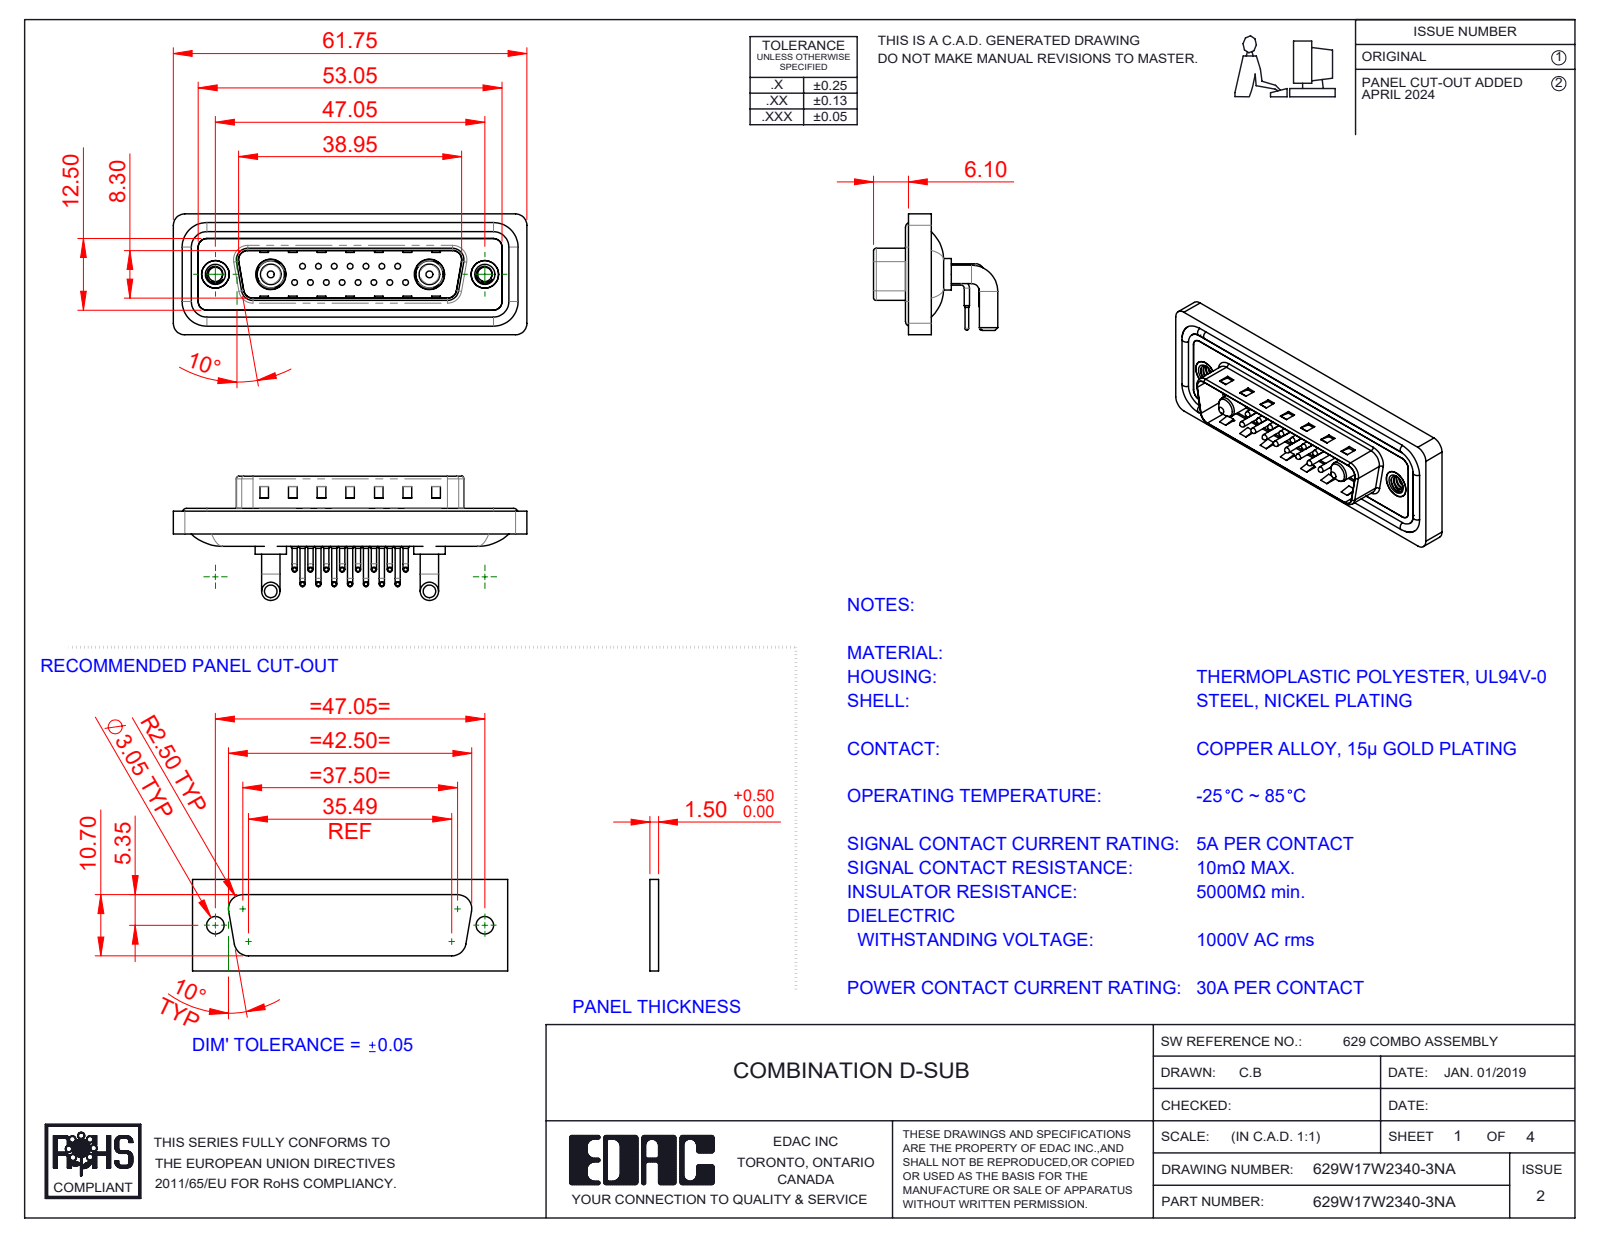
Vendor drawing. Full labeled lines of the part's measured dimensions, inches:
Part name (STEP PRODUCT): 629Combo Contact Row 2; 629Combo Contact Row 1; Power Pin_30A RA; 629Combo Shell Rear_25 Contacts (+5 more)
STEP written by: SolidWorks 2023 (CONFIG_CONTROL_DESIGN)
Units: inches
Bodies: 26 solids, 2213 faces (1189 planar, 768 cylindrical, 256 other)
Overall size (bounding box): 2.431 × 0.854 × 0.831
Volume: 0.462 in³ · Surface area: 19.6 in²
Round holes (diameter × count): ⌀0.03 ×15, ⌀0.063 ×15, ⌀0.079 ×15, ⌀0.098 ×2, ⌀0.157 ×2, ⌀0.189 ×2, ⌀0.191 ×2, ⌀0.197 ×2, ⌀0.209 ×2
Round bosses / shafts (diameter × count): ⌀0.035 ×30, ⌀0.059 ×15, ⌀0.039 ×15, ⌀0.026 ×15, ⌀0.126 ×4, ⌀0.063 ×4, ⌀0.217 ×2, ⌀0.205 ×2
Partial cylindrical surfaces — rounded edges, fillets, slot ends (radius × count): R0.059 ×18, R0.079 ×18, R0.04 ×15, R0.02 ×8, R0.063 ×8, R0.01 ×4, R0.024 ×4, R0.026 ×4
Main face-to-face distances: 0.016, 0.114, 0.031, 0.161, 0.043, 0.083, 0.063, 0.177, 0.059, 0.098
Hole centre spacings: 0.124, 0.109, 0.218, 0.327, 0.198, 0.295, 0.436, 0.198
